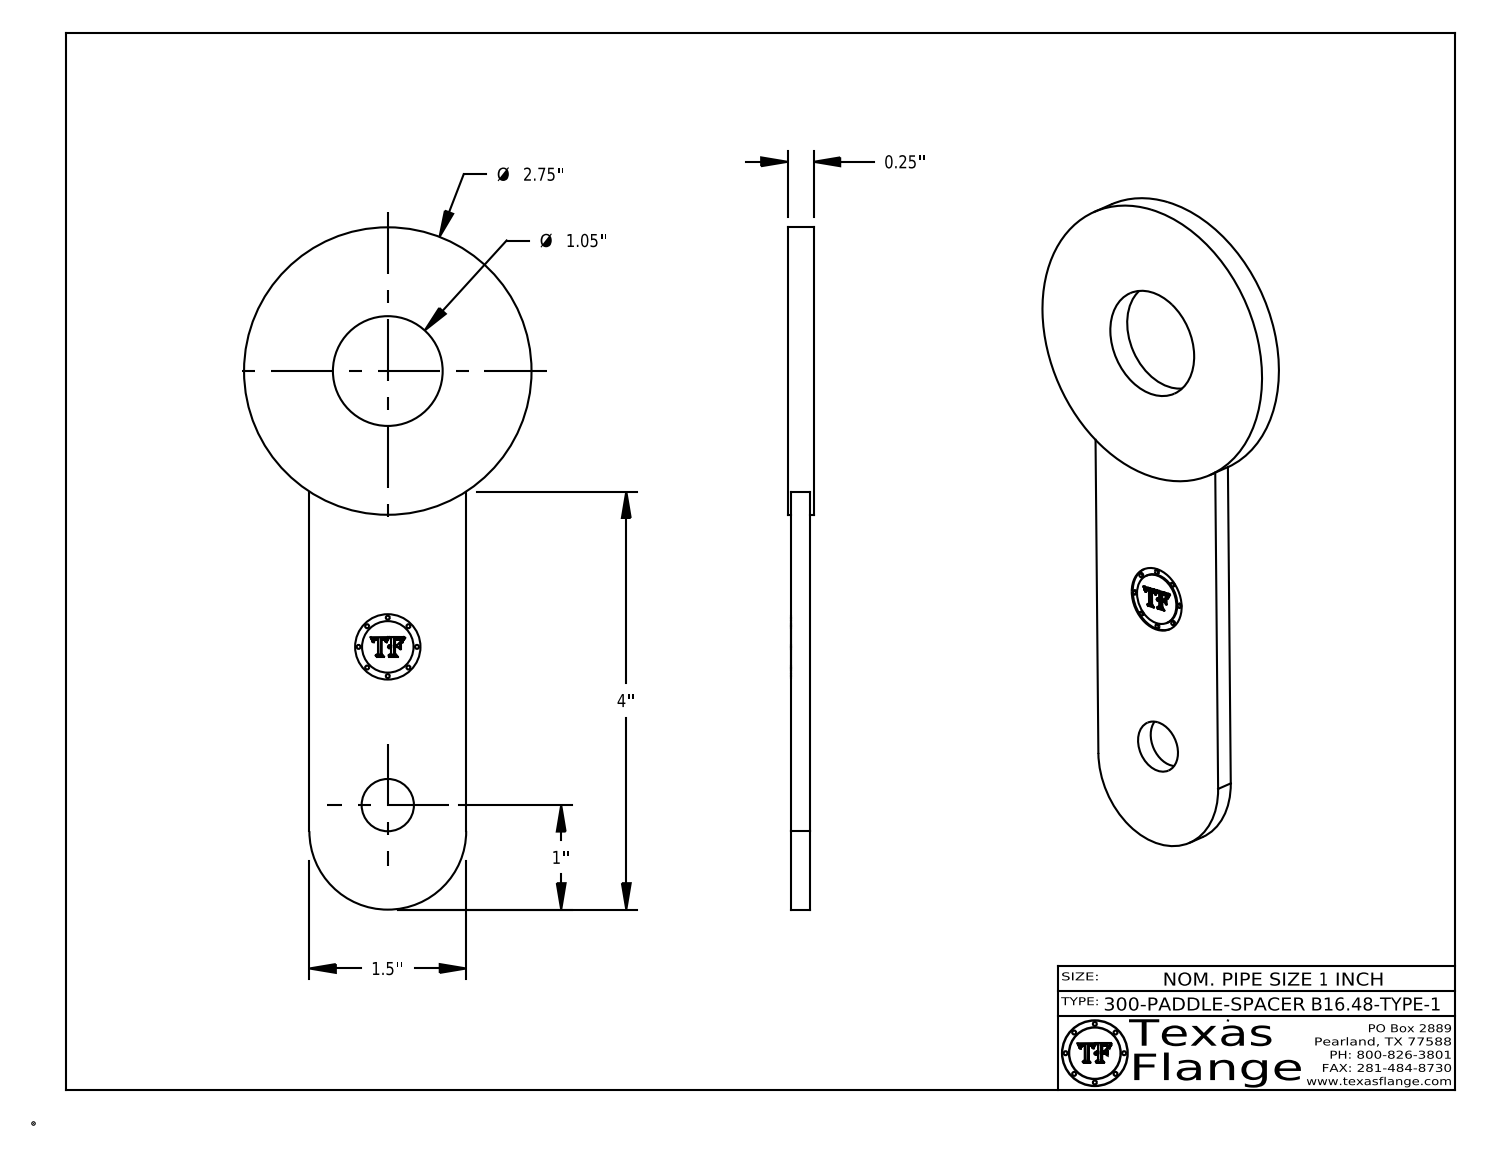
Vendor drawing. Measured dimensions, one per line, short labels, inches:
name: 1-300-PADDLE-SPACER-B16.48-TYPE-2
written by: CATIA V5 STEP AP214 (AUTOMOTIVE_DESIGN)
unit: in
bodies: 1 solid, 398 faces (371 planar, 27 cylindrical, 0 other)
size: 6.527 × 2.75 × 0.25
volume: 2.267 in³; area: 25.58 in²
holes: 1× ⌀0.5, 1× ⌀0.625, 1× ⌀1.05
bosses: 8× ⌀0.038, 1× ⌀2.75, 1× ⌀0.492
rounds: 1× R0.75
face distances: 0.219, 0.031, 0.187, 0.25, 1.5, 0.046, 0.204, 0.172, 0.015, 0.687
hole spacings: 1.514, 2.639, 4.152
